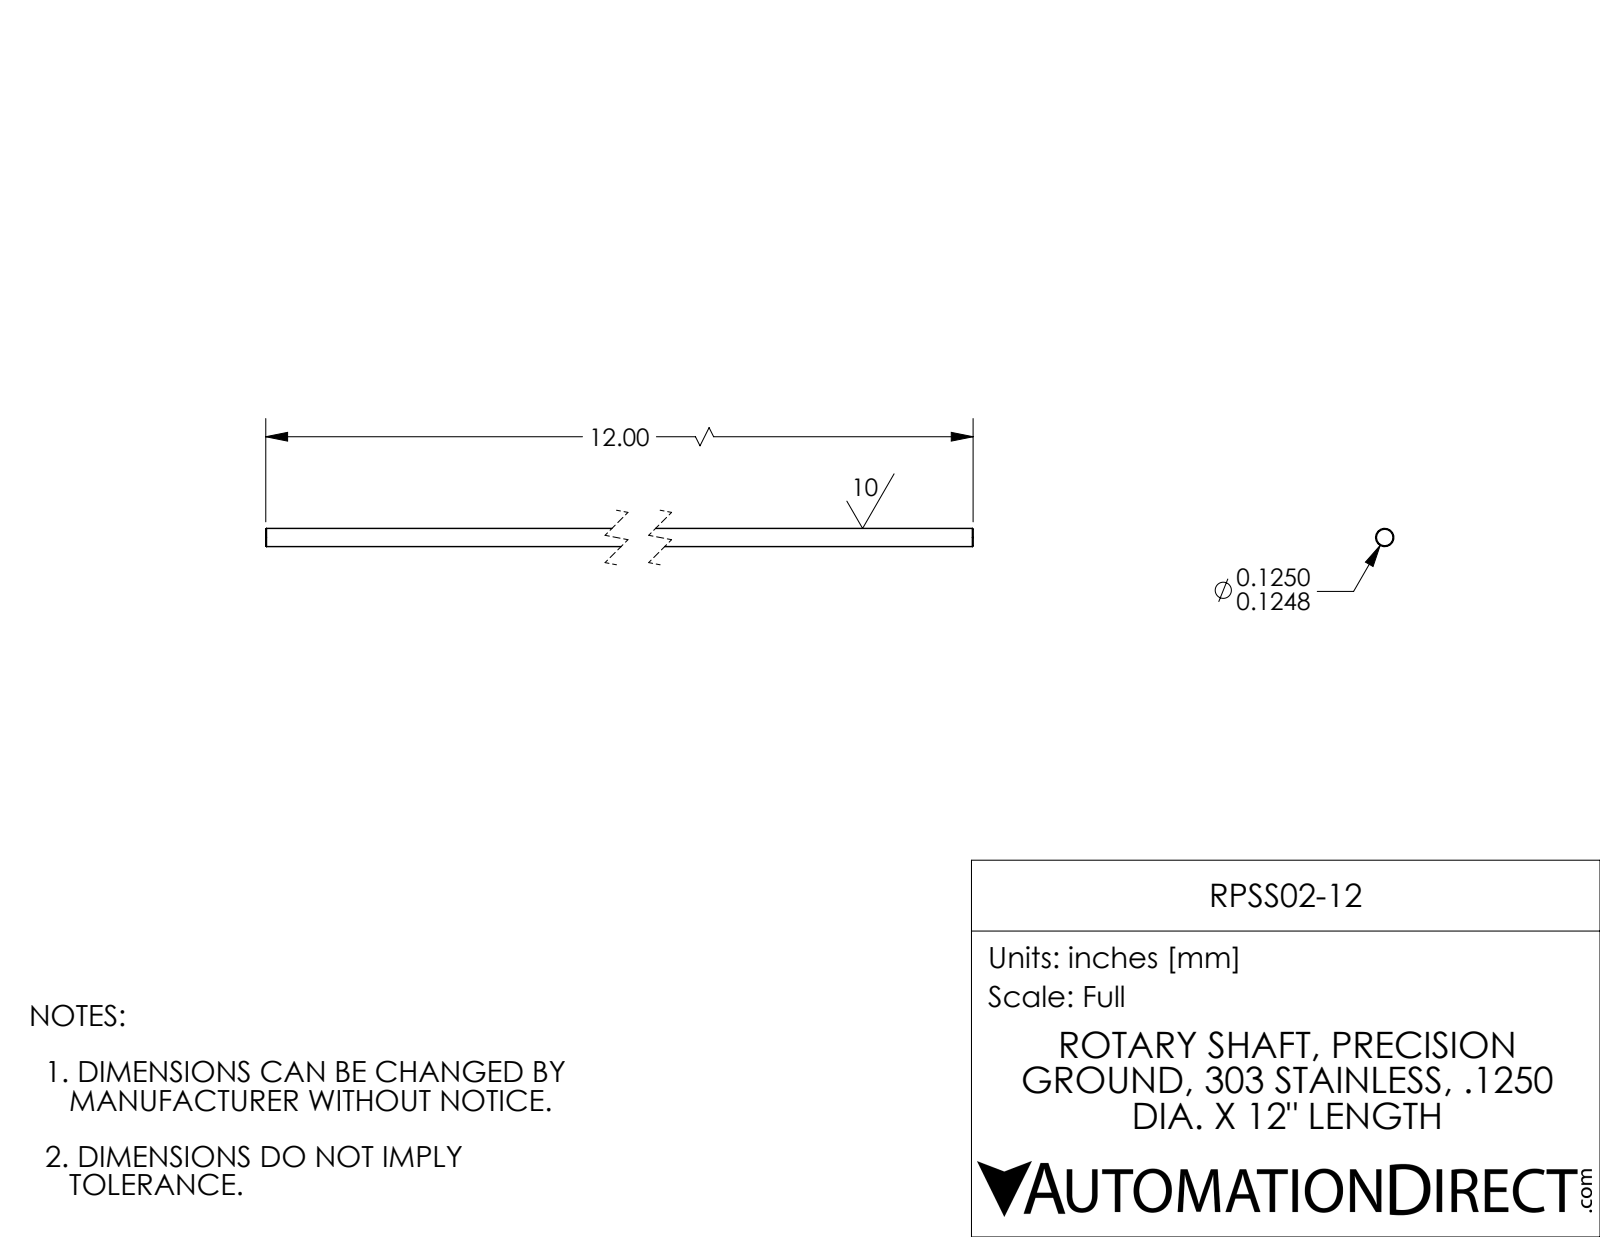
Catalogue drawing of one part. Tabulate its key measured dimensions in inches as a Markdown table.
| quantity | value |
| --- | --- |
| part name | RPSS02-12 |
| STEP written by | SolidWorks 2017 (AUTOMOTIVE_DESIGN) |
| units | inches |
| bodies | 1 solid, 8 faces (2 planar, 2 cylindrical, 4 other) |
| overall size | 12 × 0.125 × 0.125 |
| volume | 0.147 in³ |
| surface area | 4.735 in² |
| round bosses / shafts (diameter × count) | 0.125 × 1 |
| main face-to-face distances | 12 |
